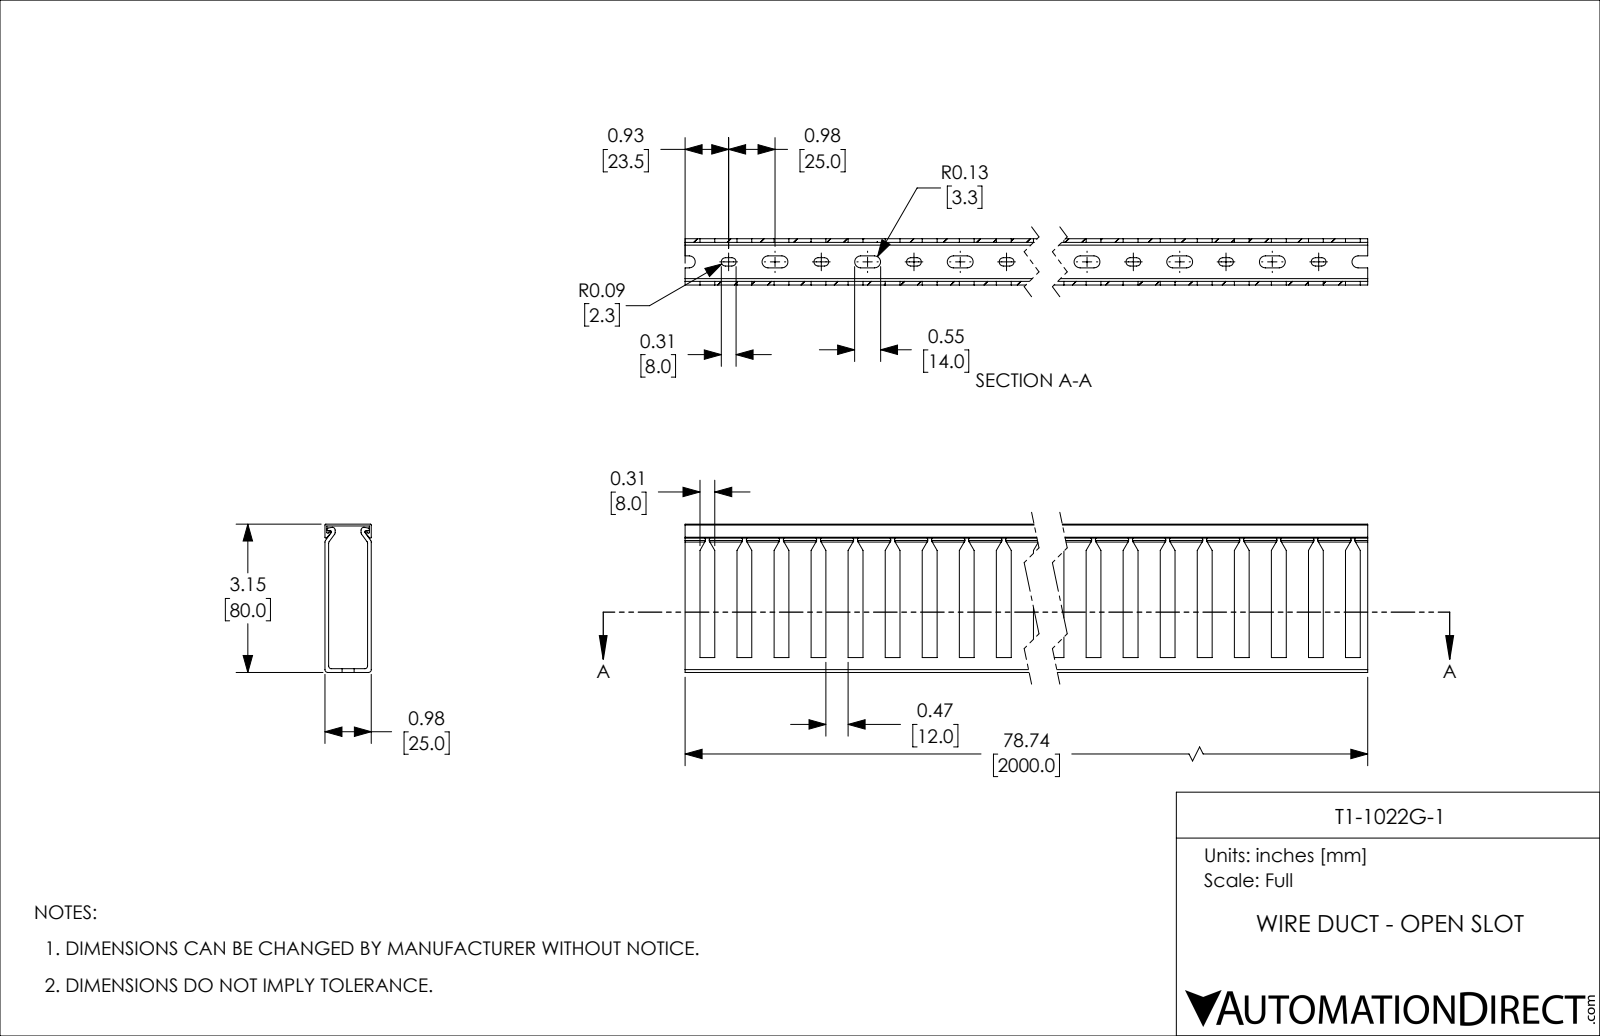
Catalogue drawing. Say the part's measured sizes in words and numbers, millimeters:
The part is named "T1-1030G-1". Its 3-D file was written by "SolidWorks 2021 (CONFIG_CONTROL_DESIGN)". It is 2 solids with 945 faces: 514 planar, 431 cylindrical and 0 other. Overall it measures 2000 by 80 by 25 millimeters. Its volume is 789 980 cubic millimeters and its surface area 883 662 square millimeters. Partial cylindrical surfaces (rounded edges, fillets, slot ends): 80 of radius 2.25, 80 of radius 3.25, 12 of radius 1.5, 8 of radius 0.5, 6 of radius 0.75. The main face-to-face distances are 2, 23, 25, 21, 1, 80, 79, 77, 78, 24.
